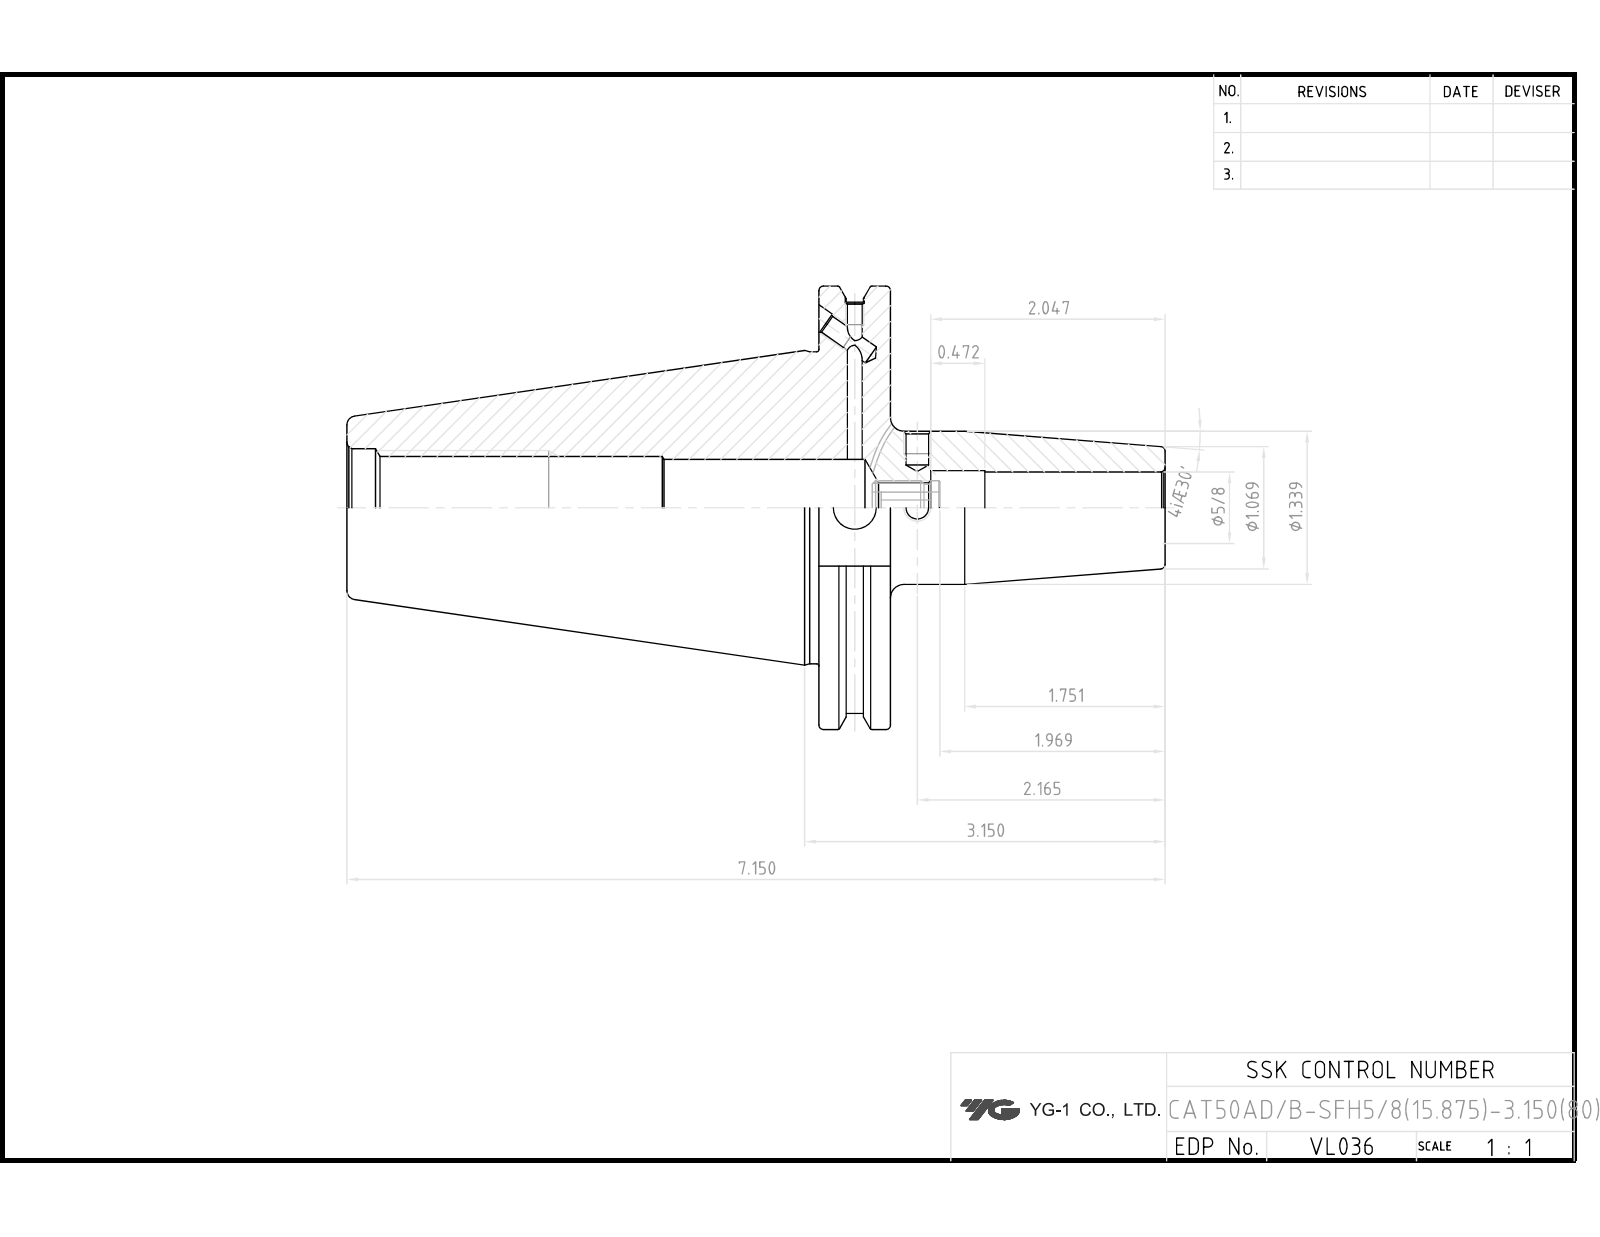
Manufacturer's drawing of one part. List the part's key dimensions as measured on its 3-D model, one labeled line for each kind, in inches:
Part name (STEP PRODUCT): LO-CAT50ADB-SFH15.875-80
STEP written by: Autodesk Inventor 2025 (AUTOMOTIVE_DESIGN)
Units: inches
Bodies: 1 solid, 84 faces (37 planar, 26 cylindrical, 21 other)
Overall size (bounding box): 7.15 × 3.875 × 3.728
Volume: 22.11 in³ · Surface area: 81.77 in²
Round holes (diameter × count): ⌀0.128 ×2, ⌀0.163 ×2, ⌀0.165 ×2, ⌀0.197 ×2, ⌀0.375 ×1, ⌀0.43 ×1, ⌀0.625 ×1, ⌀0.672 ×1, ⌀0.865 ×1, ⌀1.031 ×1
Round bosses / shafts (diameter × count): ⌀3.875 ×1, ⌀3.594 ×1, ⌀2.726 ×1, ⌀1.339 ×1
Main face-to-face distances: 0.625, 4.125, 4.75, 2.875, 1.02, 7.15, 3.025, 2.4, 4.363, 0.238
